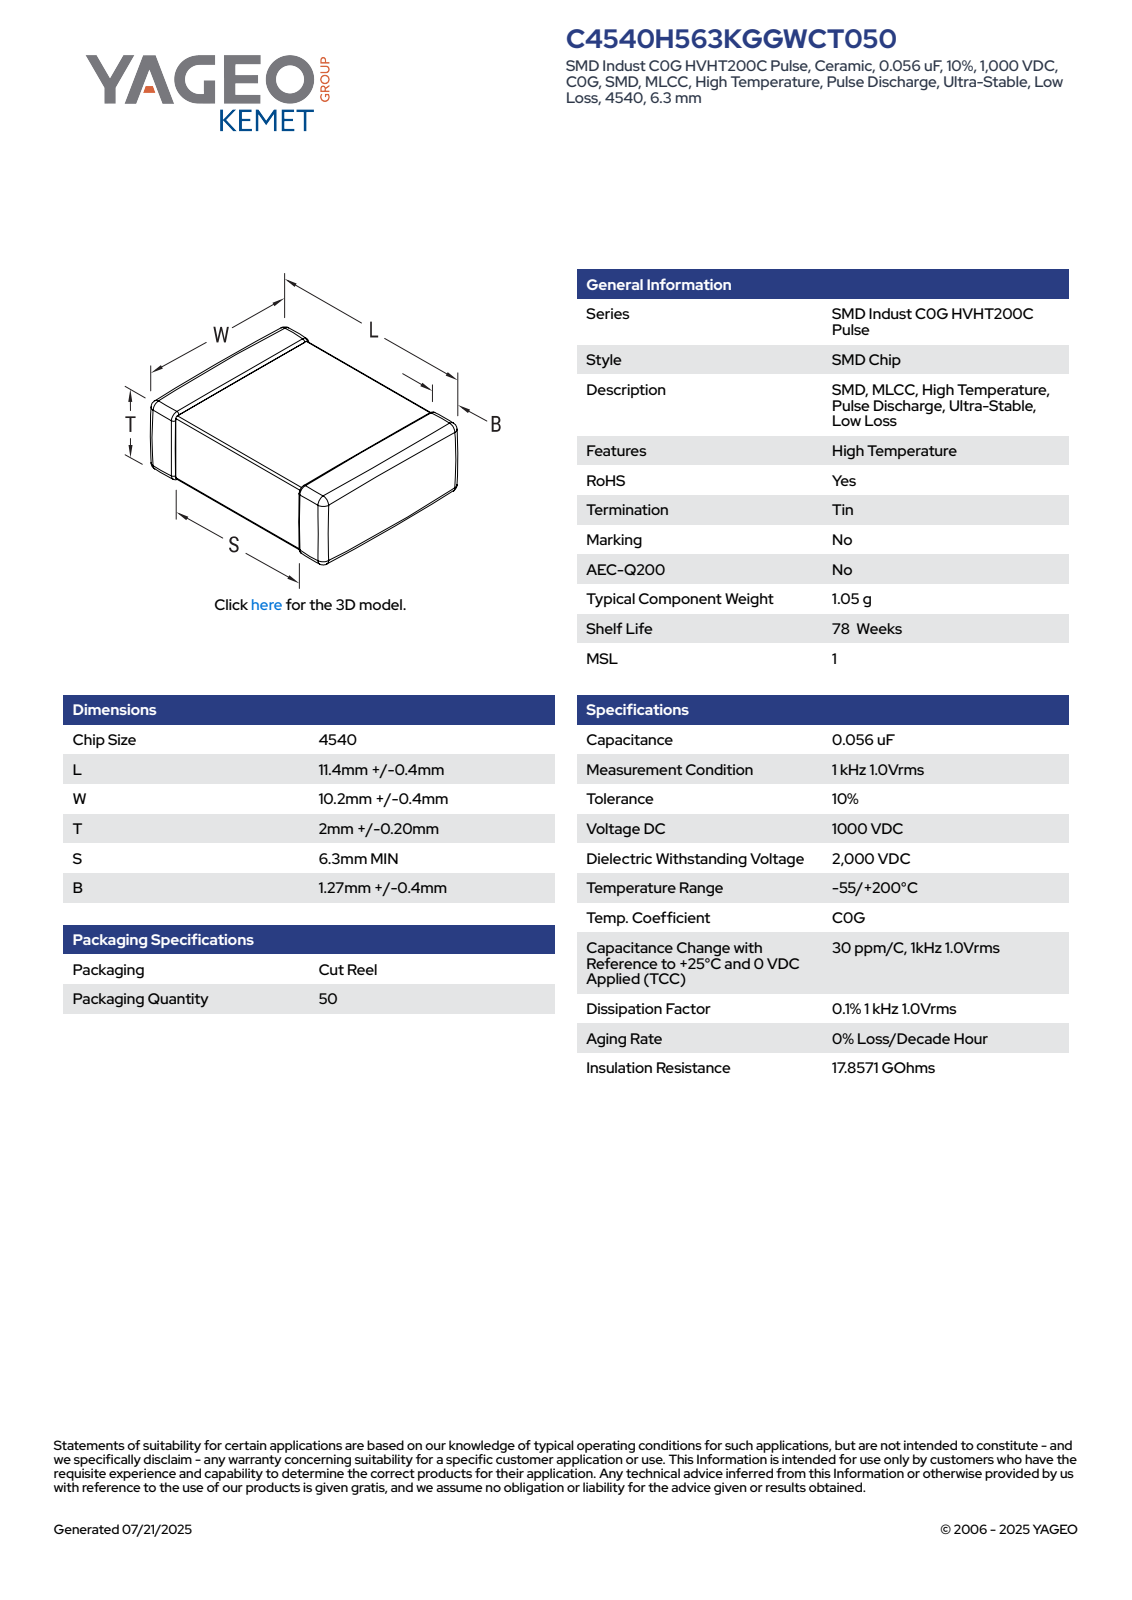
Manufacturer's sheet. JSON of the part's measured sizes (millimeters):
{"part_name": "CCS_CCSTD_4540_L11.8W10.6T2.2B1.27", "step_written_by": "SolidWorks 2021 (AUTOMOTIVE_DESIGN)", "units": "millimeters", "bodies": {"solids": 4, "faces": 125, "planar": 71, "cylindrical": 38, "other": 16}, "overall_size": [11.8, 10.6, 2.2], "volume_mm3": 228, "surface_area_mm2": 345, "partial_cylinders_radius": [[0.22, 24]], "face_to_face_distances": [1.76, 1.98, 2.2, 11.8, 10.16, 10.38, 10.6, 4.81, 6.99, 6.37]}
